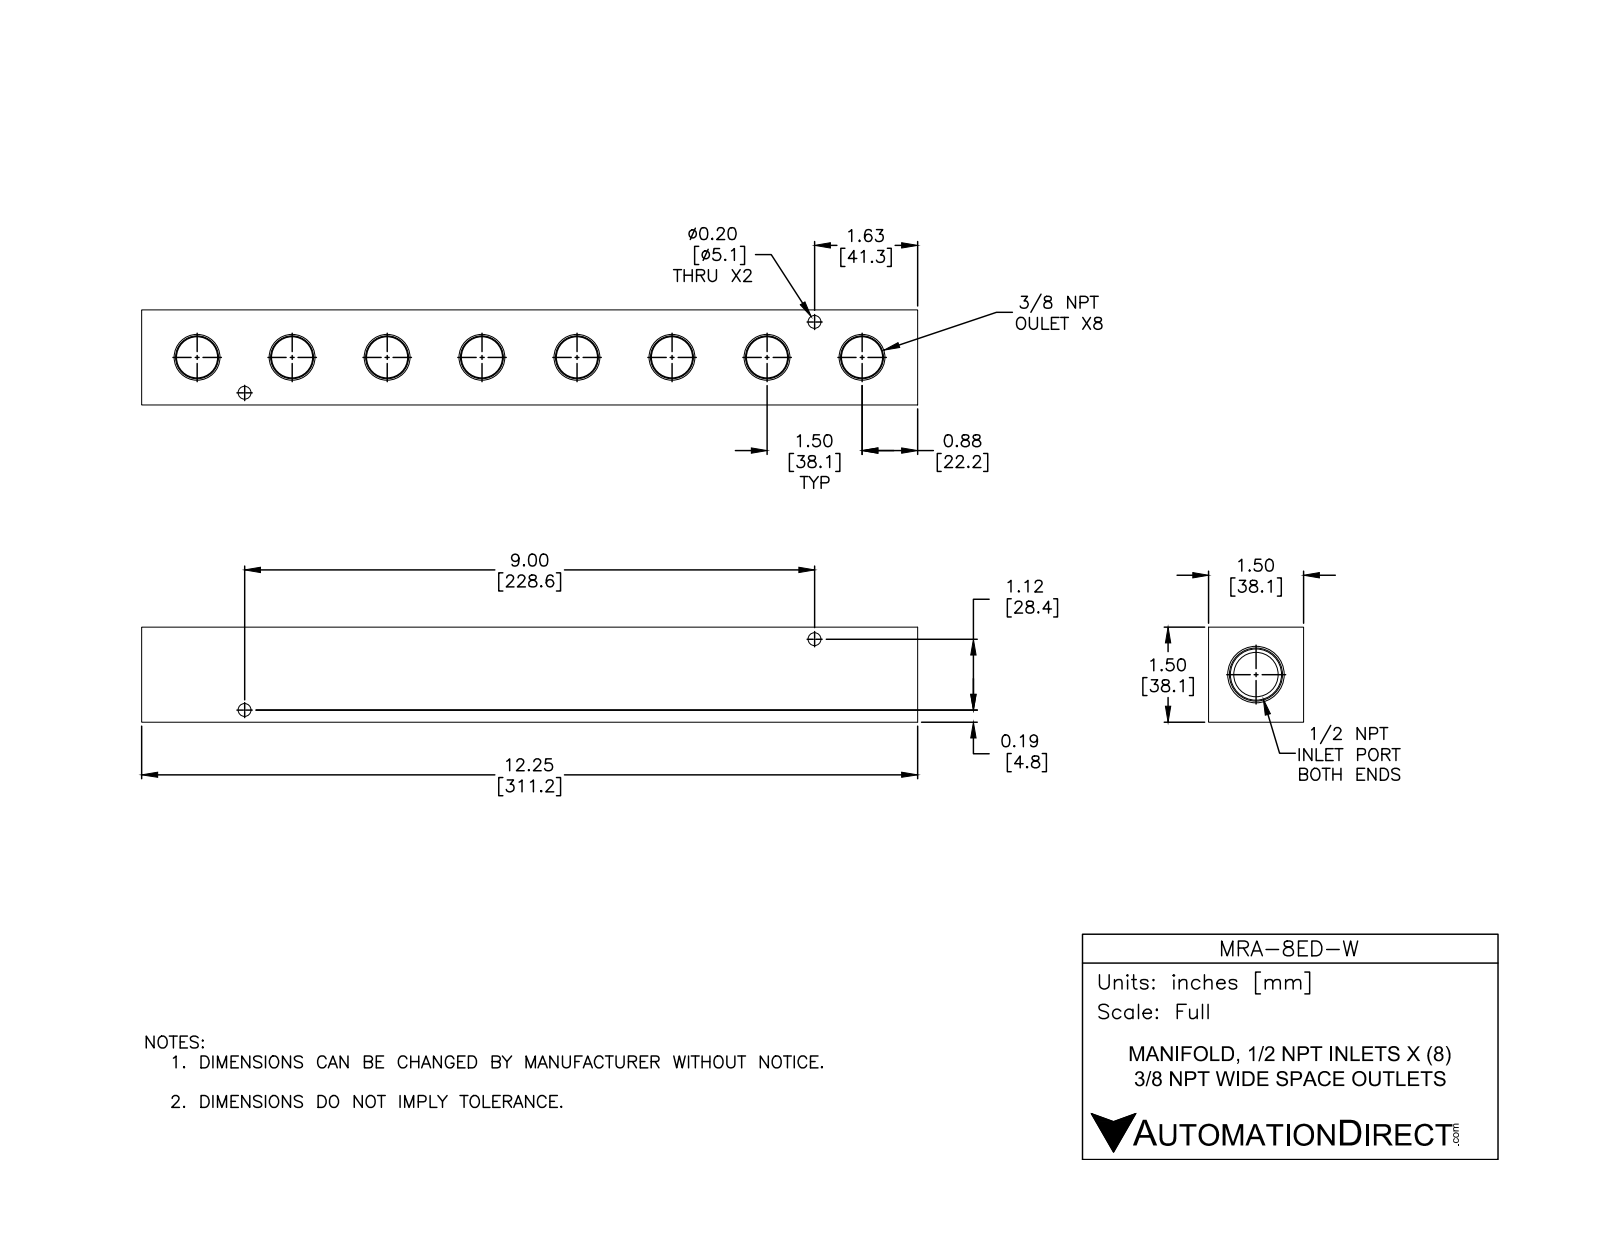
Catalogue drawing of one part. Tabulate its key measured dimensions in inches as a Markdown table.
| quantity | value |
| --- | --- |
| part name | MRA-8ED-W |
| STEP written by | SolidWorks 2015 (CONFIG_CONTROL_DESIGN) |
| units | inches |
| bodies | 1 solid, 98 faces (24 planar, 34 cylindrical, 40 other) |
| overall size | 12.25 × 1.5 × 1.5 |
| volume | 21.29 in³ |
| surface area | 110.5 in² |
| round holes (diameter × count) | 0.562 × 8, 0.2 × 4, 0.703 × 1 |
| main face-to-face distances | 1.5, 12.25, 1.09, 0.41, 0.53, 11.72, 11.19 |
| hole center spacings | 1.5, 3, 4.5, 6, 7.5, 0.932, 0.94, 9 |
